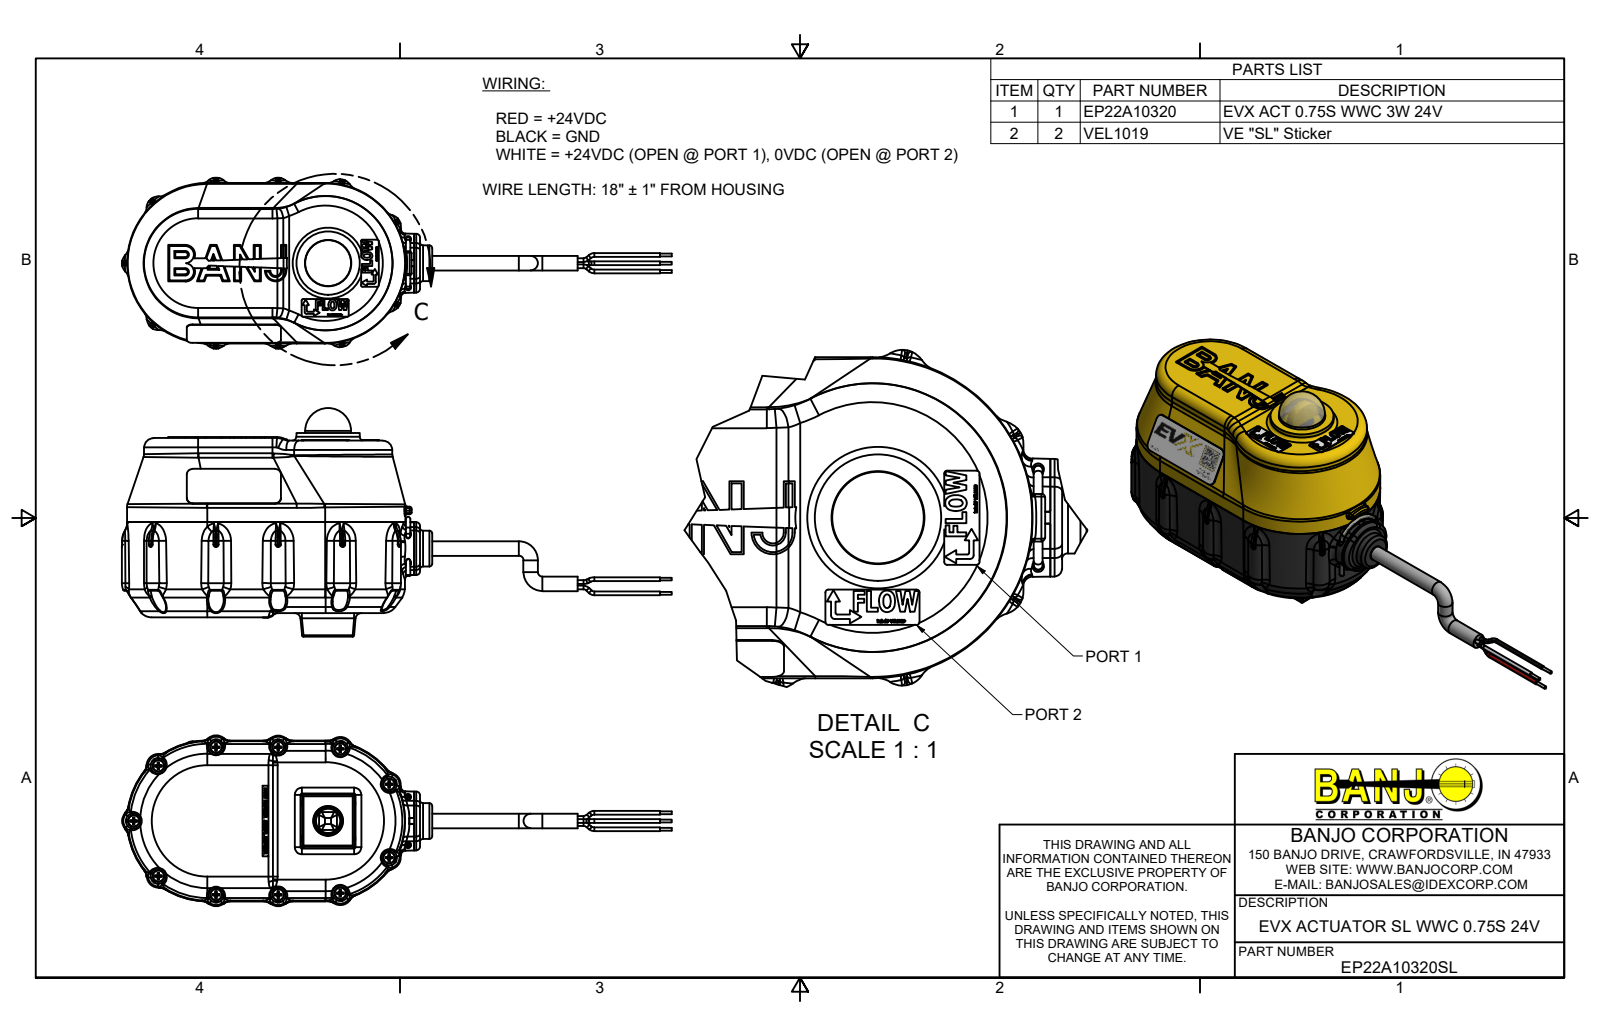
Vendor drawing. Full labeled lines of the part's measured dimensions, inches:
Part name (STEP PRODUCT): EP22A10320SL; EP22A10320; B61905PPHS; B632038PM (+8 more)
STEP written by: Autodesk Inventor 2021 (AUTOMOTIVE_DESIGN)
Units: inches
Bodies: 75 solids, 10528 faces (2923 planar, 2944 cylindrical, 4661 other)
Overall size (bounding box): 11.685 × 4.853 × 3.63
Volume: 31.12 in³ · Surface area: 406.2 in²
Round holes (diameter × count): ⌀0.095 ×11, ⌀0.15 ×11, ⌀0.08 ×7, ⌀0.107 ×4, ⌀0.126 ×4, ⌀0.136 ×4, ⌀0.148 ×4, ⌀0.15 ×4, ⌀0.17 ×4, ⌀0.105 ×2, ⌀0.118 ×2, ⌀0.123 ×2
Round bosses / shafts (diameter × count): ⌀0.25 ×17, ⌀0.08 ×15, ⌀0.14 ×11, ⌀0.108 ×11, ⌀0.085 ×11, ⌀0.058 ×6, ⌀0.27 ×4, ⌀0.219 ×4
Partial cylindrical surfaces — rounded edges, fillets, slot ends (radius × count): R0.013 ×180, R0.04 ×145, R0.01 ×84, R0.02 ×71, R0.005 ×54, R0.08 ×28, R0.03 ×26, R0.1 ×22
Main face-to-face distances: 0.1, 2.565, 0.211, 0.06, 0.151, 1.685, 1.836, 1.896, 2.465, 0.78
Hole centre spacings: 1.283, 1.513, 2.69, 2.849, 3.789, 0.487, 0.668, 1.226
